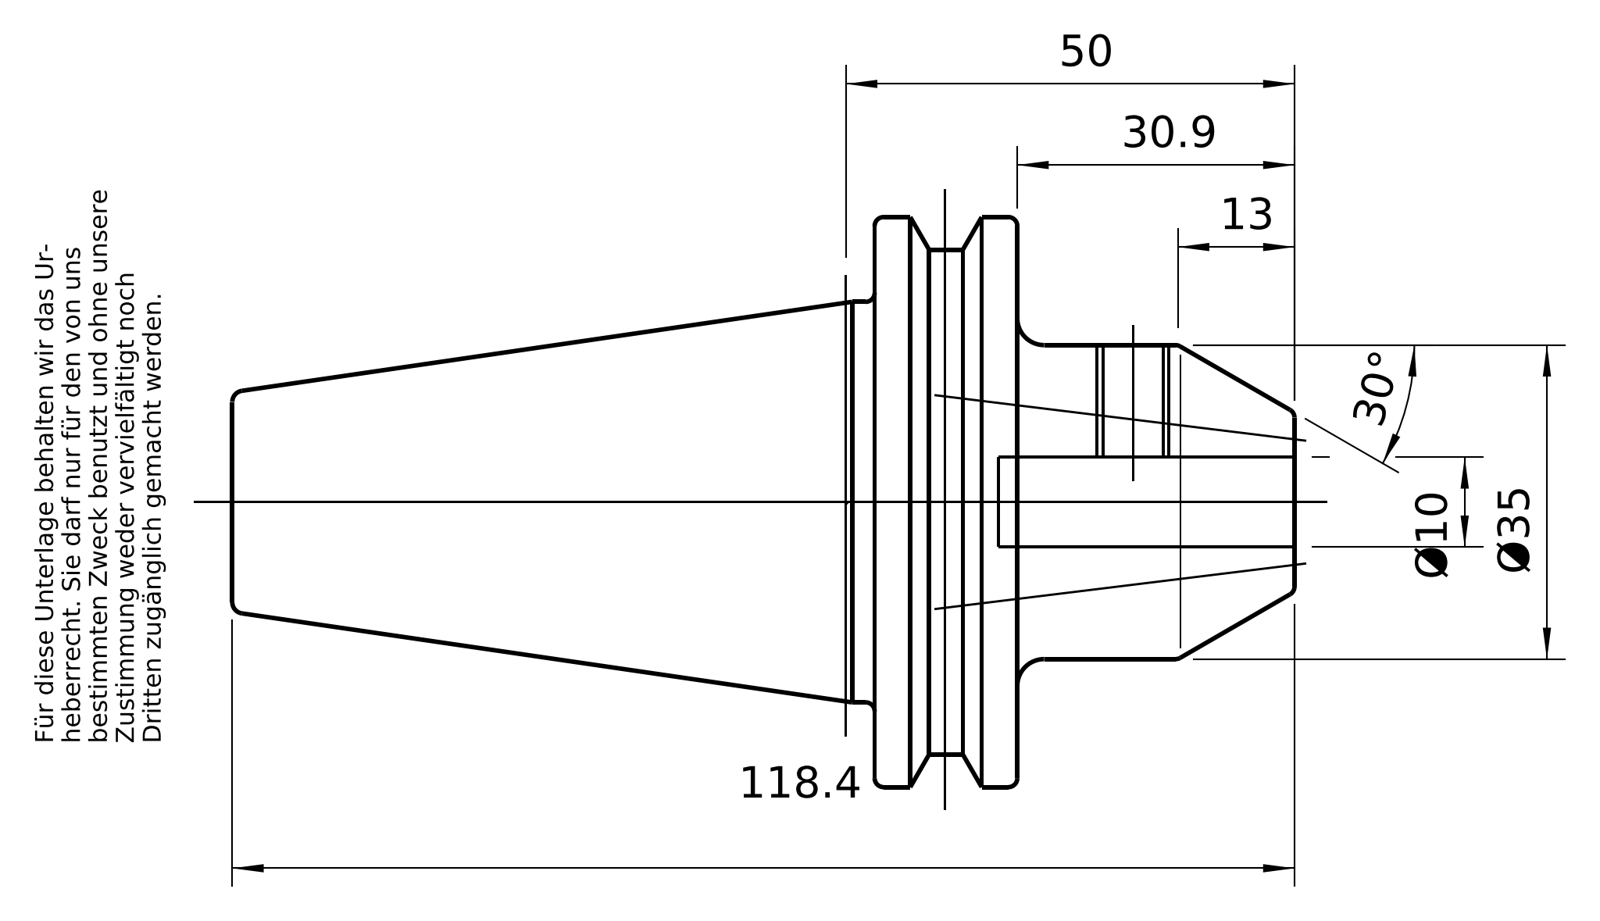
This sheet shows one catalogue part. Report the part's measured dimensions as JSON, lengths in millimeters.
{"part_name": "40-300-10", "step_written_by": "PRO/ENGINEER BY PARAMETRIC TECHNOLOGY CORPORATION, 2010430 (CONFIG_CONTROL_DESIGN)", "units": "millimeters", "bodies": {"solids": 1, "faces": 99, "planar": 21, "cylindrical": 28, "other": 50}, "overall_size": [118.25, 63.52, 61.42], "volume_mm3": 127642, "surface_area_mm2": 24215, "round_holes": [[10, 2], [8.5, 1], [13.84, 1], [17.01, 1], [17.5, 1]], "round_bosses_or_shafts": [[43.75, 1], [35, 1], [16.01, 1]], "partial_cylinders_radius": [[1.35, 1], [28, 1], [31.76, 1]], "face_to_face_distances": [15.85, 47.4, 46.8, 30.95, 16.2, 71.45, 87.3, 118.25, 83.25, 11.8]}
